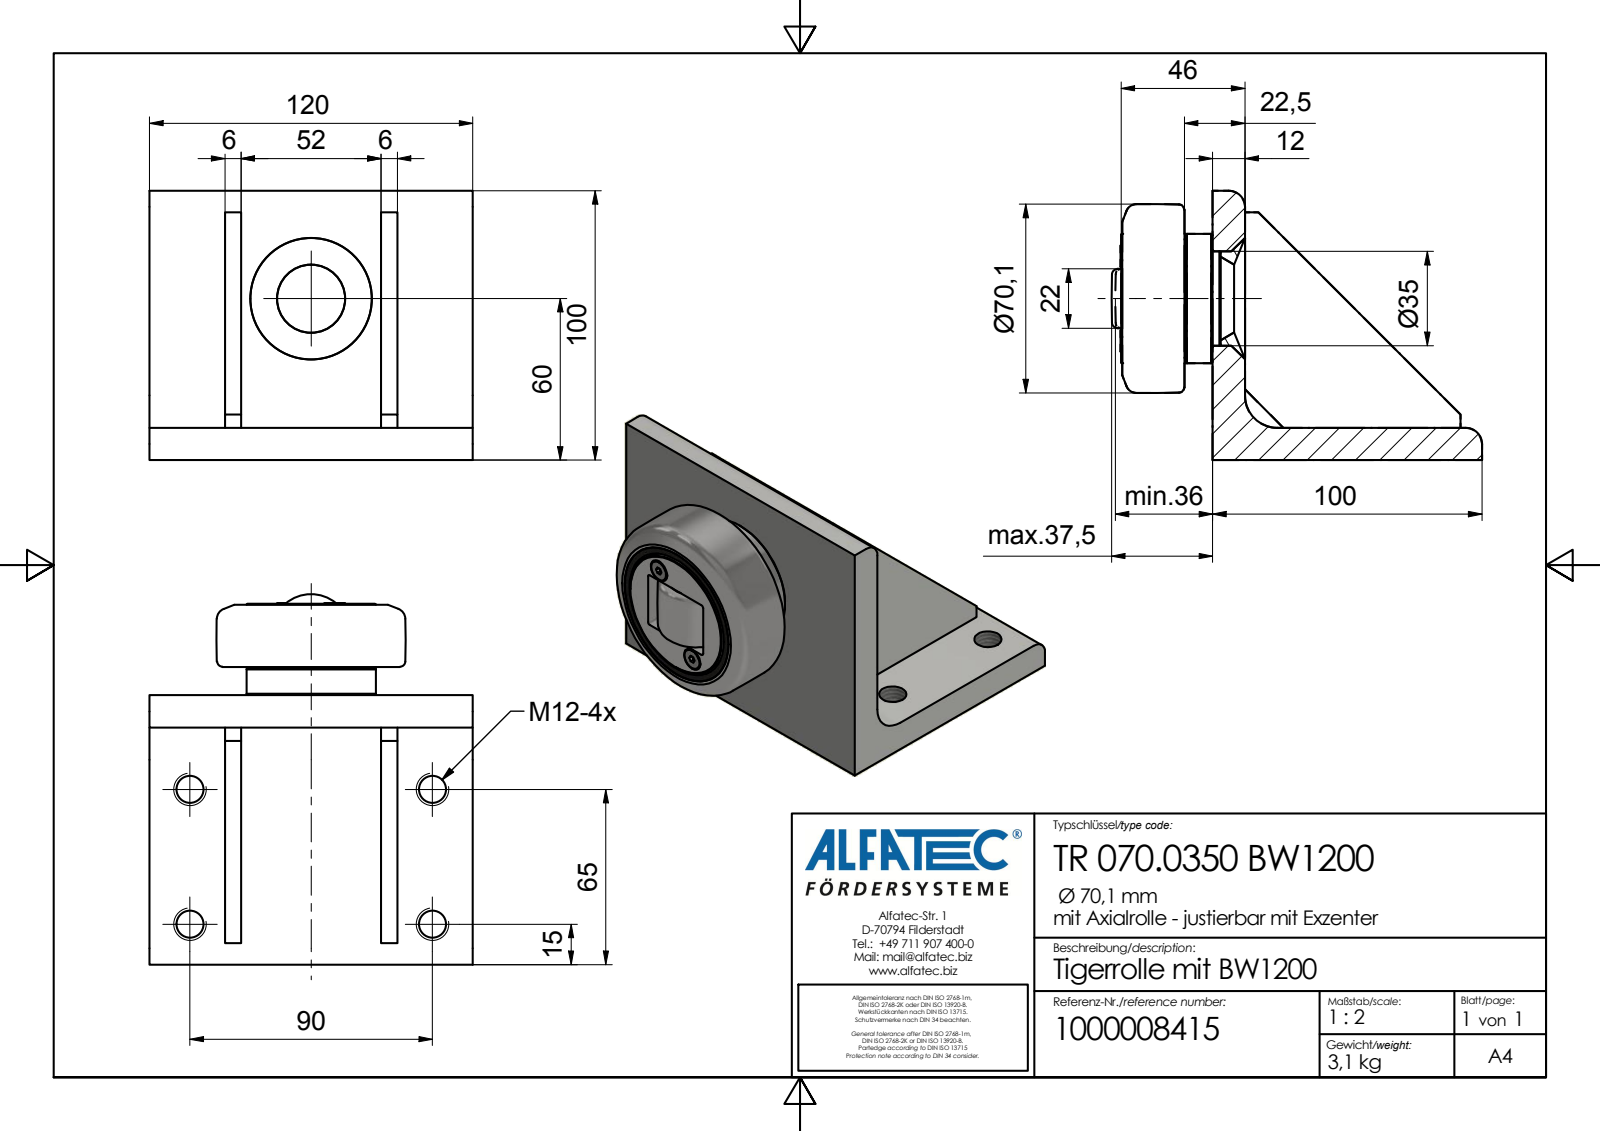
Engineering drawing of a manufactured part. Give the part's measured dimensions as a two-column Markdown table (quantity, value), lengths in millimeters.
| quantity | value |
| --- | --- |
| part name | TR 070.0350 BW1200_Kontur |
| STEP written by | Autodesk Inventor 2020 (AP242_MANAGED_MODEL_BASED_3D_ENGINEERING_MIM_LF) |
| units | millimeters |
| bodies | 1 solid, 81 faces (50 planar, 18 cylindrical, 13 other) |
| overall size | 137.5 × 120 × 100 |
| volume | 413 783 mm³ |
| surface area | 76 701 mm² |
| round holes (diameter × count) | 10.11 × 4 |
| round bosses / shafts (diameter × count) | 7.8 × 2, 48 × 1 |
| partial cylindrical surfaces (radius × count) | 1 × 4, 6 × 2, 11 × 1, 12 × 1 |
| main face-to-face distances | 12, 58, 6, 34, 92, 28, 86, 64, 52, 120 |
| hole center spacings | 50, 90, 102.96 |
